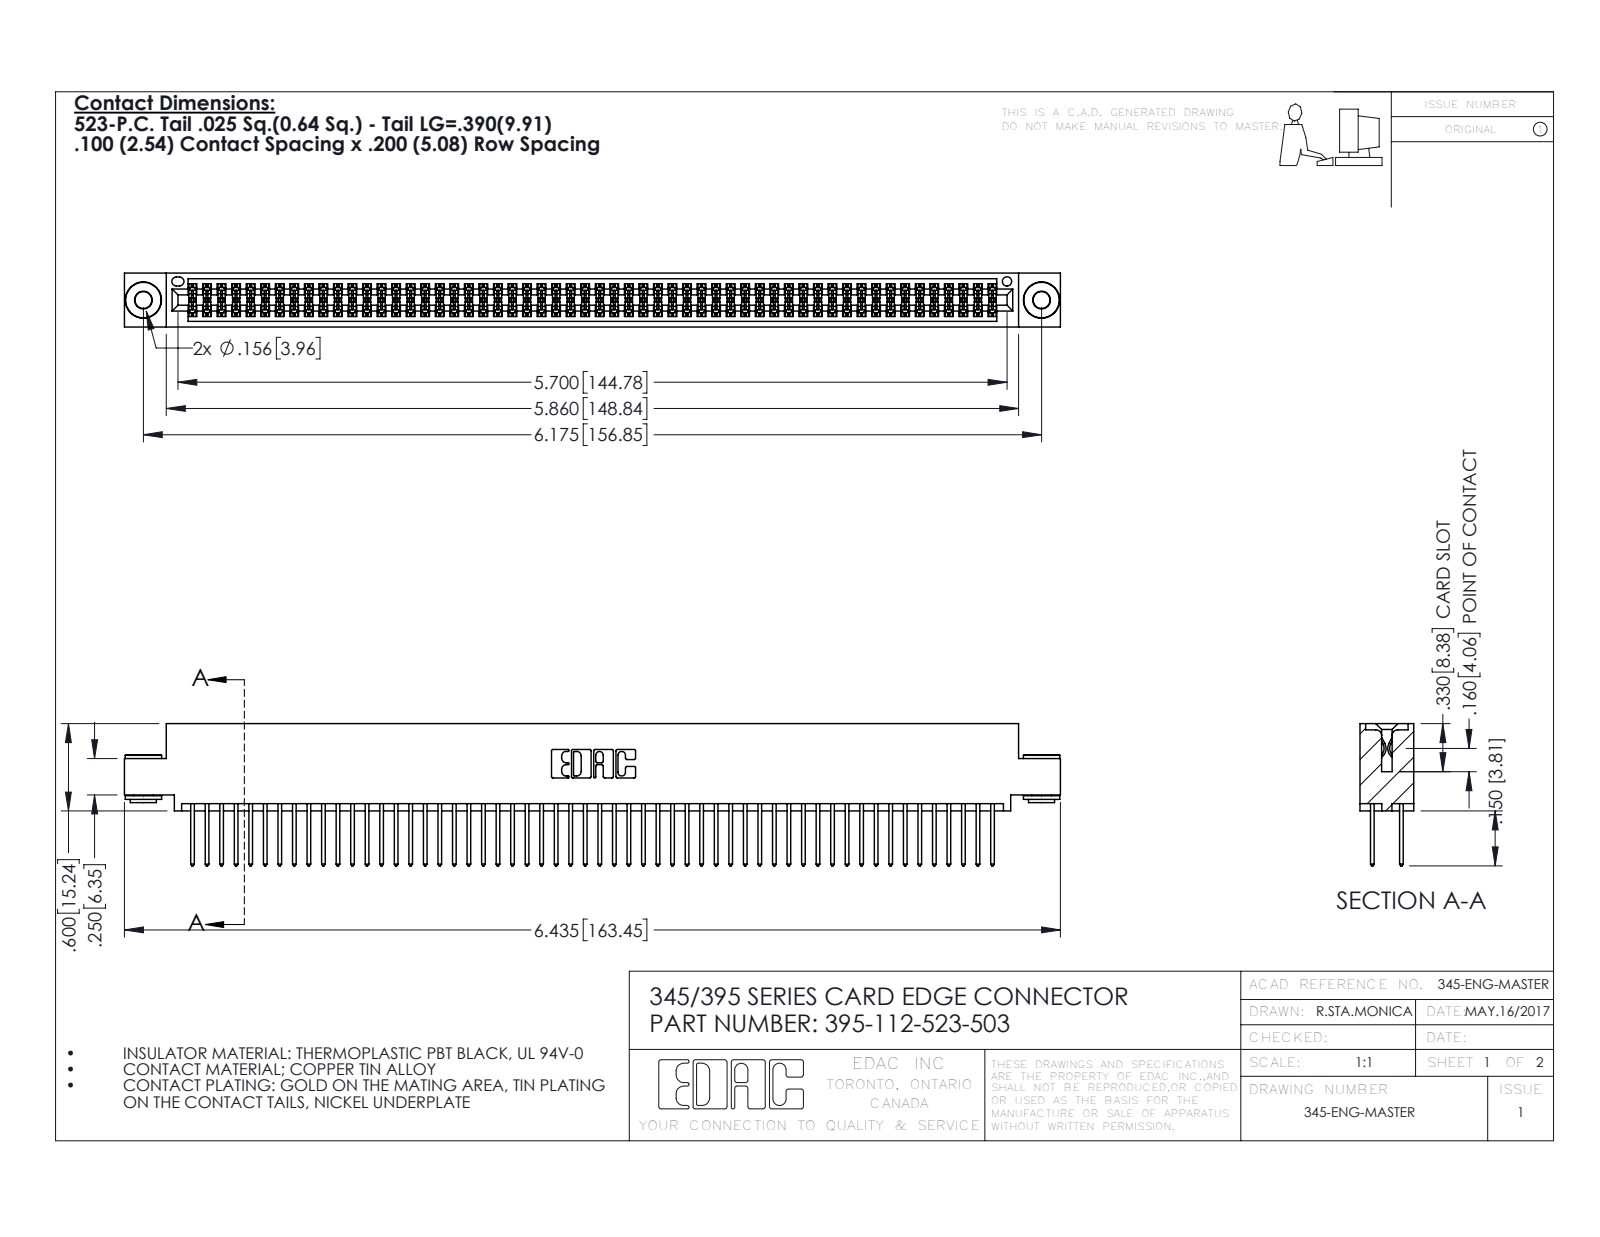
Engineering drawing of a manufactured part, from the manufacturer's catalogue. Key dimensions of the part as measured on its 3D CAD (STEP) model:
Part name (STEP PRODUCT): 395-112-523-503; 345-250-002_345-250-002-102; 345 Part_0.110 Offset - 0.156 Dia-TH; 345-292-001_345-293-123
STEP written by: SolidWorks 2016 (CONFIG_CONTROL_DESIGN)
Units: inches
Bodies: 115 solids, 5768 faces (3790 planar, 1970 cylindrical, 8 other)
Overall size (bounding box): 6.435 × 0.977 × 0.37
Volume: 0.988 in³ · Surface area: 39.56 in²
Round holes (diameter × count): ⌀0.116 ×2, ⌀0.156 ×2, ⌀0.064 ×1
Round bosses / shafts (diameter × count): ⌀0.25 ×2, ⌀0.18 ×2, ⌀0.136 ×2
Partial cylindrical surfaces — rounded edges, fillets, slot ends (radius × count): R0.006 ×168, R0.01 ×112, R0.01 ×22, R0.007 ×6, R0.031 ×6, R0.026 ×3, R0.014 ×2, R0.019 ×2
Main face-to-face distances: 0.072, 0.298, 0.2, 0.025, 0.098, 0.272, 0.37, 0.225, 0.175, 0.149
Hole centre spacings: 0.27, 5.939, 6.175
